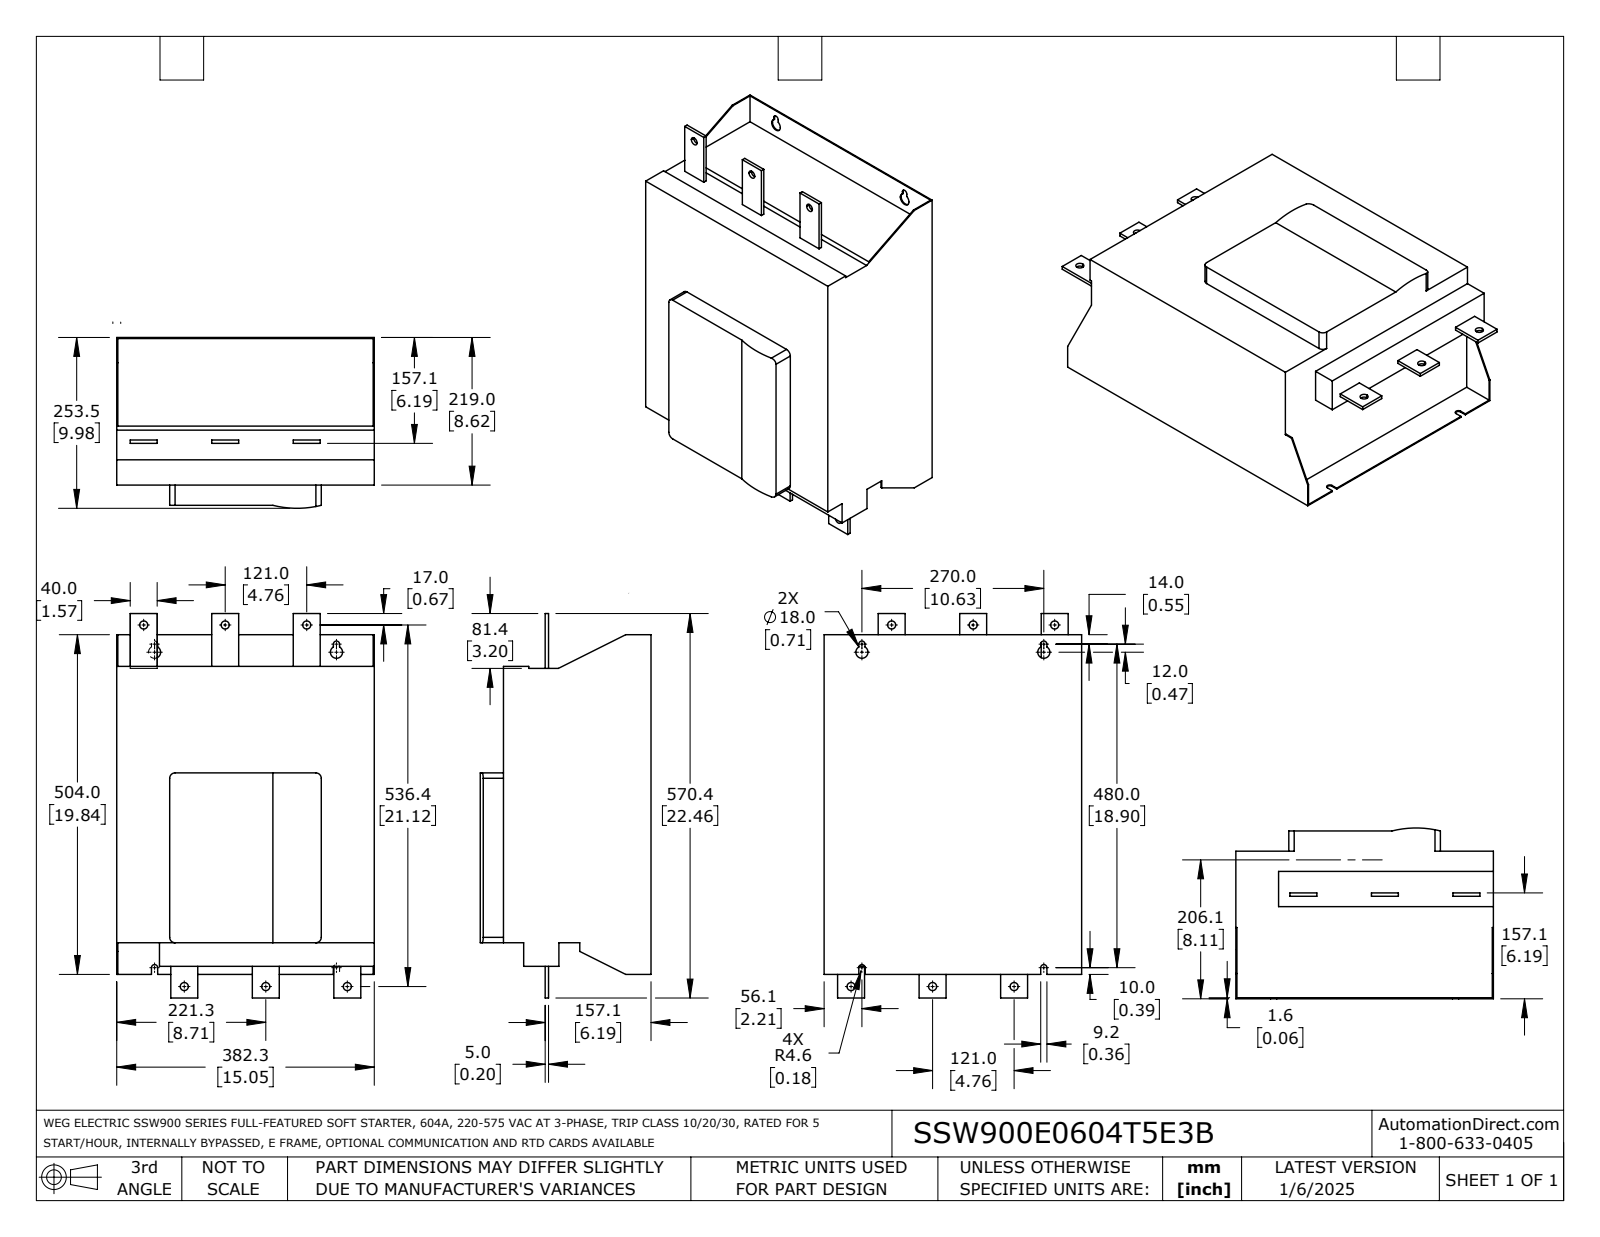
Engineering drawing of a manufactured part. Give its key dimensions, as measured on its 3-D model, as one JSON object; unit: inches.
{"part_name": "SSW900E0604T5E3B", "step_written_by": "SolidWorks 2021 (AUTOMOTIVE_DESIGN)", "units": "inches", "bodies": {"solids": 1, "faces": 97, "planar": 70, "cylindrical": 27, "other": 0}, "overall_size": [22.457, 15.049, 9.979], "volume_in3": 2243, "surface_area_in2": 1320, "round_holes": [[0.472, 6], [0.709, 2]], "partial_cylinders_radius": [[0.181, 4], [0.315, 4], [5.788, 1]], "face_to_face_distances": [8.622, 15.049, 16.142, 0.063, 1.181, 9.803, 8.559, 9.74, 1.378, 16.024], "hole_center_spacings": [4.764, 21.251, 9.528, 21.253, 22.291, 1.713, 2.356, 4.424]}
